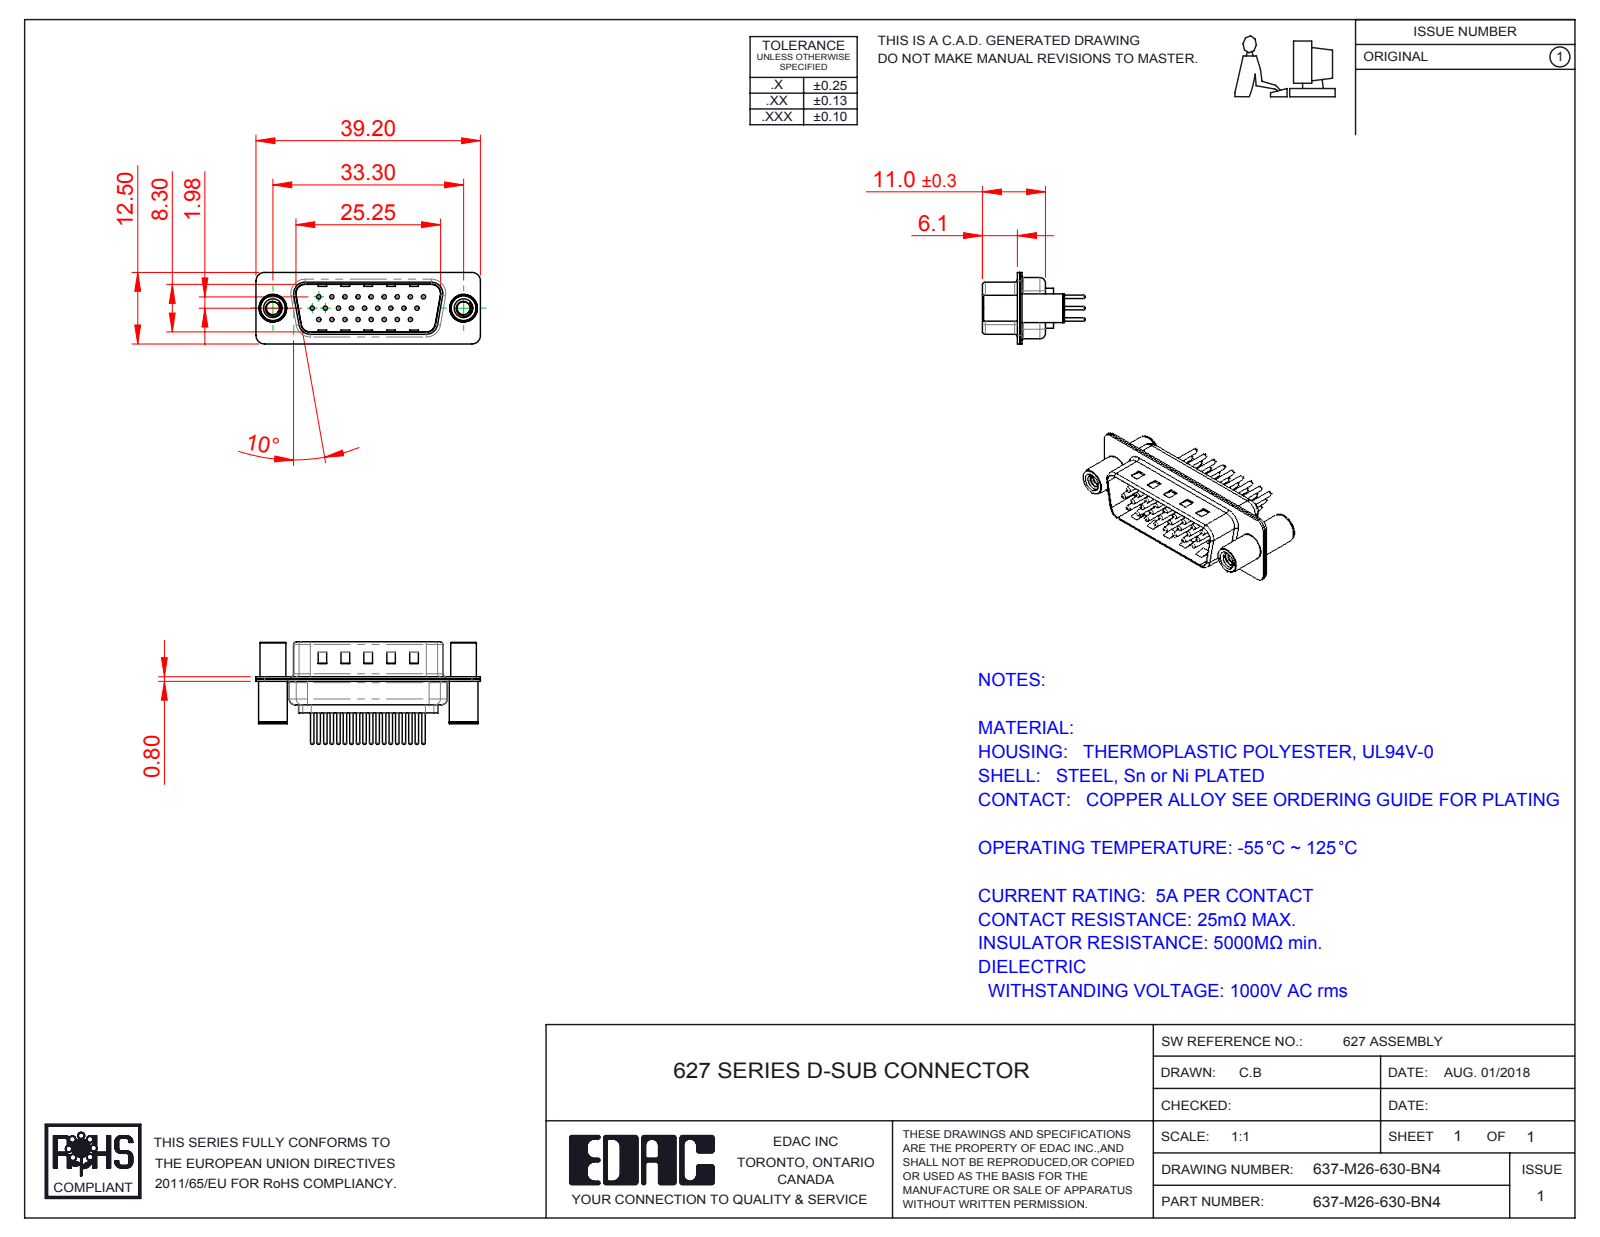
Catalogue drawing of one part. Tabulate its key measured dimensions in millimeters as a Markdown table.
| quantity | value |
| --- | --- |
| part name | 637M Housing_26 Contacts; 637M Shell Rear_26 Contacts; 637M Contact Row 1_30; 637M Shell Front_26 Contacts (+4 more) |
| STEP written by | SolidWorks 2016 (CONFIG_CONTROL_DESIGN) |
| units | millimeters |
| bodies | 31 solids, 1388 faces (327 planar, 549 cylindrical, 512 other) |
| overall size | 39.2 × 17.9 × 12.5 |
| volume | 2 196 mm³ |
| surface area | 6 280 mm² |
| round holes (diameter × count) | 0.75 × 26, 1.6 × 26, 2 × 26, 2.26 × 2, 3.26 × 2, 4 × 2, 4.8 × 2 |
| round bosses / shafts (diameter × count) | 1.5 × 26, 0.6 × 26, 5 × 2, 4.9 × 2, 4.5 × 2 |
| partial cylindrical surfaces (radius × count) | 1.5 × 16, 2 × 12, 0.5 × 8, 1.6 × 8, 0.25 × 4, 0.6 × 4, 0.65 × 4, 0.9 × 4 |
| main face-to-face distances | 0.4, 0.8, 9.5, 9.1, 8.7, 9.9, 6.3, 0.75, 5.5, 0.35 |
| hole center spacings | 3.96, 2.28, 4.57, 6.05, 2.29, 8.24, 6.86, 10.48 |
